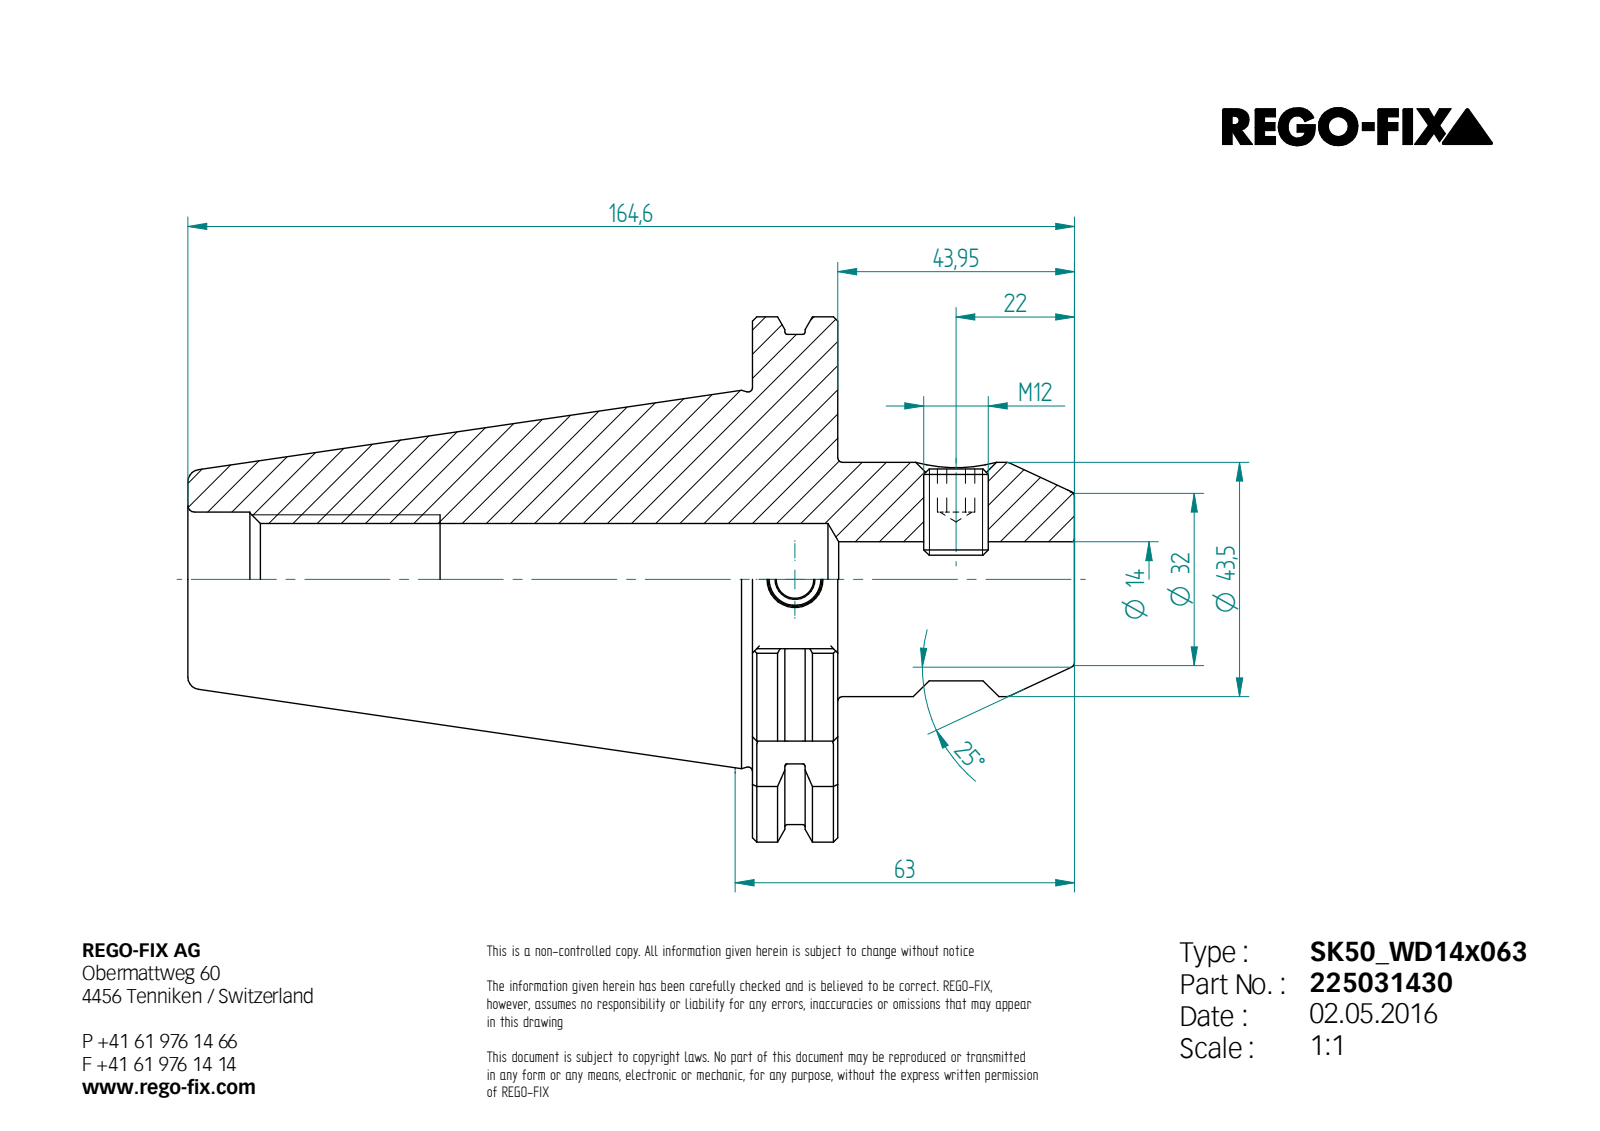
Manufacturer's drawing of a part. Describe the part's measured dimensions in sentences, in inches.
Its 3-D file was written by "Unknown (AUTOMOTIVE_DESIGN)". It is 2 solids with 119 faces: 58 planar, 23 cylindrical and 38 other. Overall it measures 6.48 by 3.839 by 3.684 inches. Its volume is 22.86 cubic inches and its surface area 80.03 square inches. Round holes: 1 of diameter 0.276, 1 of diameter 0.394, 1 of diameter 0.398, 1 of diameter 0.551, 1 of diameter 0.817, 1 of diameter 0.984. Round bosses or shafts: 1 of diameter 3.583, 1 of diameter 1.713, 1 of diameter 0.472. Partial cylindrical surfaces (rounded edges, fillets, slot ends): 5 of radius 0.02, 1 of radius 1.919. The main face-to-face distances are 0.624, 2.354, 1.73, 4.126, 4.75, 6.48, 2.866, 1.012, 0.234, 1.246.
